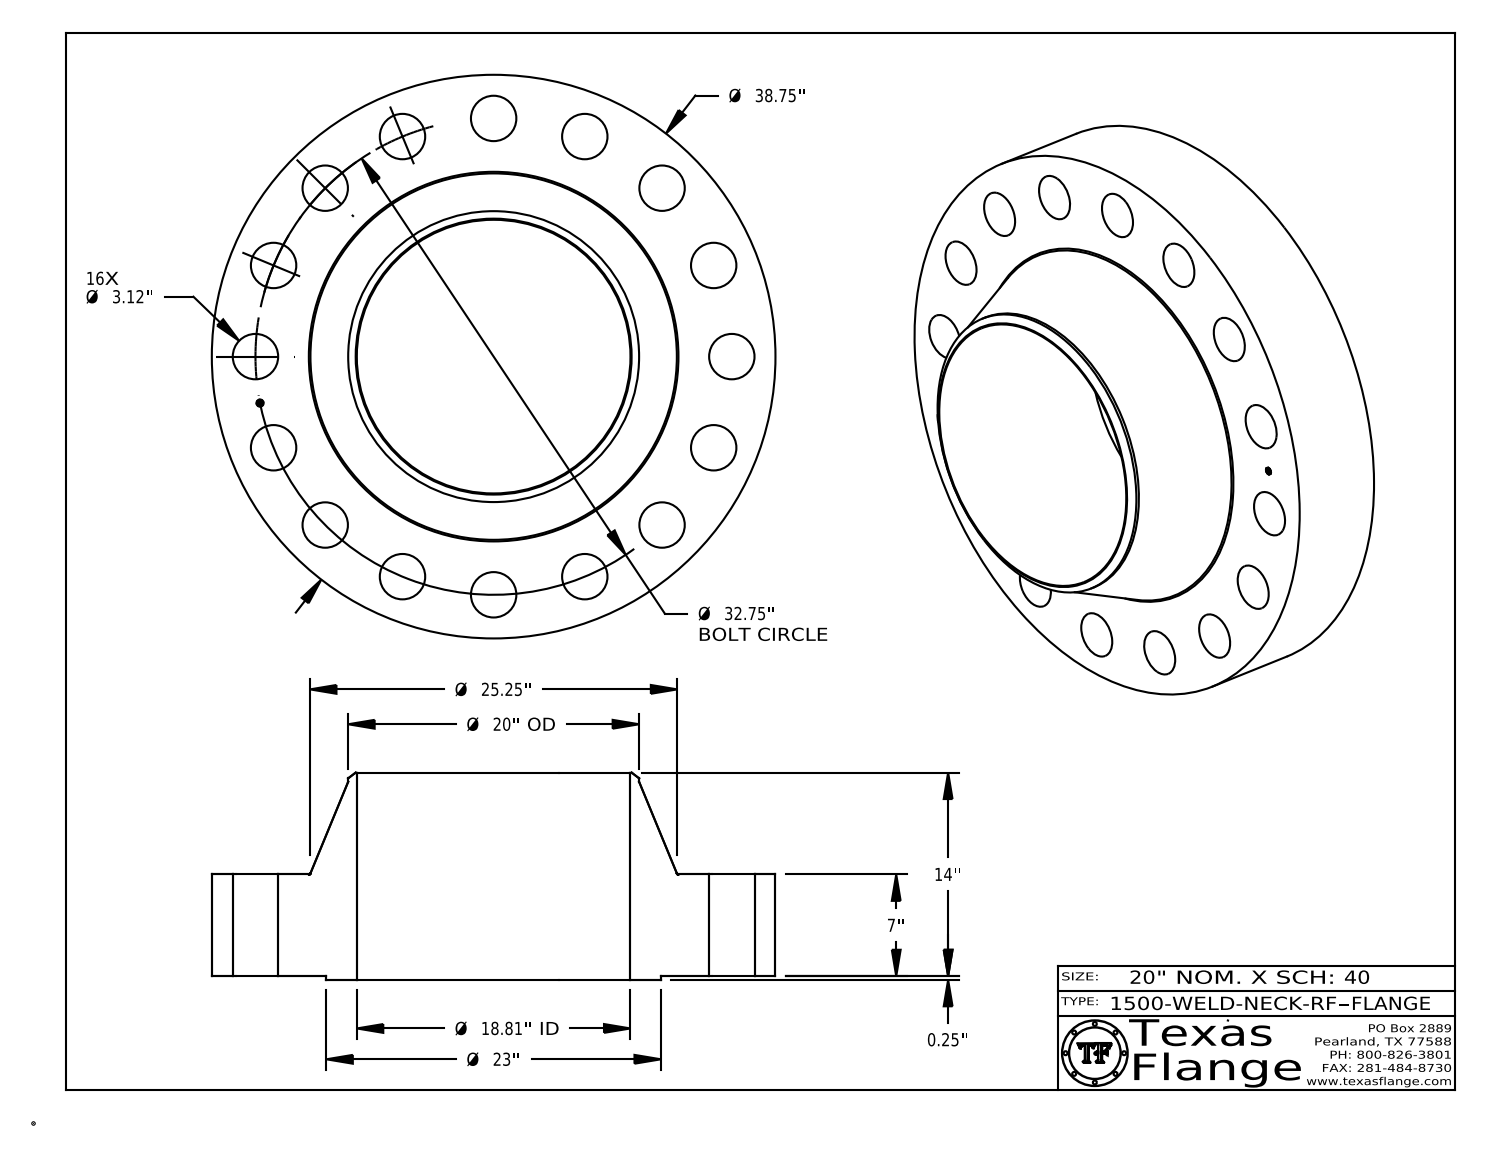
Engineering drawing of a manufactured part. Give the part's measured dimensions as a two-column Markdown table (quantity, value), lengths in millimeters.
| quantity | value |
| --- | --- |
| part name | 1500-WELD-NECK-RF |
| STEP written by | CATIA V5 STEP AP214 (AUTOMOTIVE_DESIGN) |
| units | millimeters |
| bodies | 1 solid, 435 faces (369 planar, 60 cylindrical, 6 other) |
| overall size | 984.3 × 984.3 × 362 |
| volume | 103 300 000 mm³ |
| surface area | 3 028 000 mm² |
| round holes (diameter × count) | 79.2 × 16, 12.6 × 1, 477.8 × 1 |
| round bosses / shafts (diameter × count) | 0.8 × 8, 984.3 × 1, 584.2 × 1, 508 × 1, 9.9 × 1 |
| main face-to-face distances | 177.8, 6.4, 184.2, 362, 355.6, 183.8, 177.4, 0.4, 178.2, 3.8 |
| hole center spacings | 462.2, 415.9, 318.3, 588.2, 768.5, 162.3, 162.3, 691.6 |
